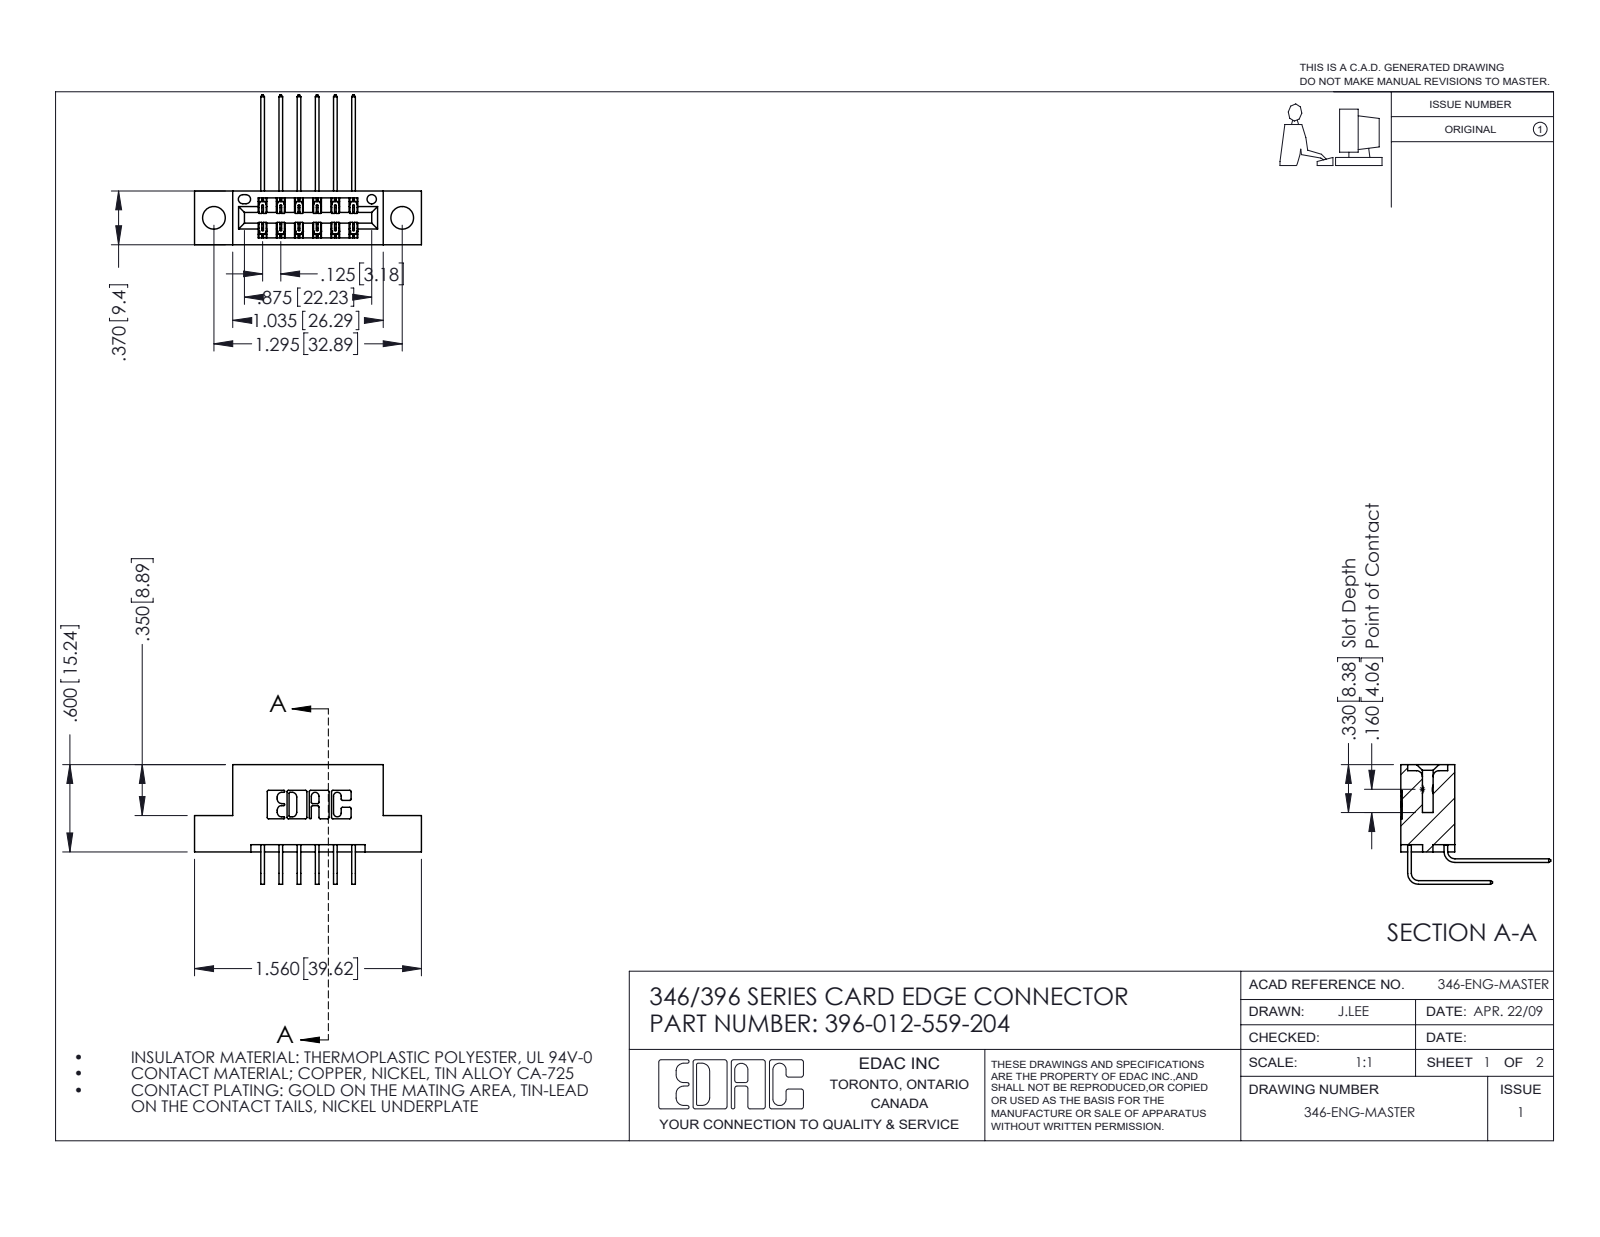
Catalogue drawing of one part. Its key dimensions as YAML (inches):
part_name: "396-012-559-204; 345-292-001_558 559 Tail - 1; 345-292-001_559 Tail - 2; 346 Part_Flush Mounting Lugs - 0.156 Dia-TH"
step_written_by: "SolidWorks 2016 (CONFIG_CONTROL_DESIGN)"
units: inches
bodies: {solids: 13, faces: 770, planar: 520, cylindrical: 250, other: 0}
overall_size: [1.56, 1.03, 0.823]
volume: 0.218
surface_area: 6.945
round_holes:
  - {diameter: 0.156, count: 2}
  - {diameter: 0.064, count: 1}
partial_cylinders:
  - {radius: 0.01, count: 22}
  - {radius: 0.006, count: 18}
  - {radius: 0.007, count: 6}
  - {radius: 0.031, count: 6}
  - {radius: 0.026, count: 3}
  - {radius: 0.014, count: 2}
  - {radius: 0.022, count: 2}
  - {radius: 0.024, count: 2}
face_to_face_distances: [0.25, 0.048, 0.322, 0.37, 0.025, 0.298, 0.072, 0.125, 0.148, 0.222]
hole_center_spacings: [0.246, 1.092, 1.295]
